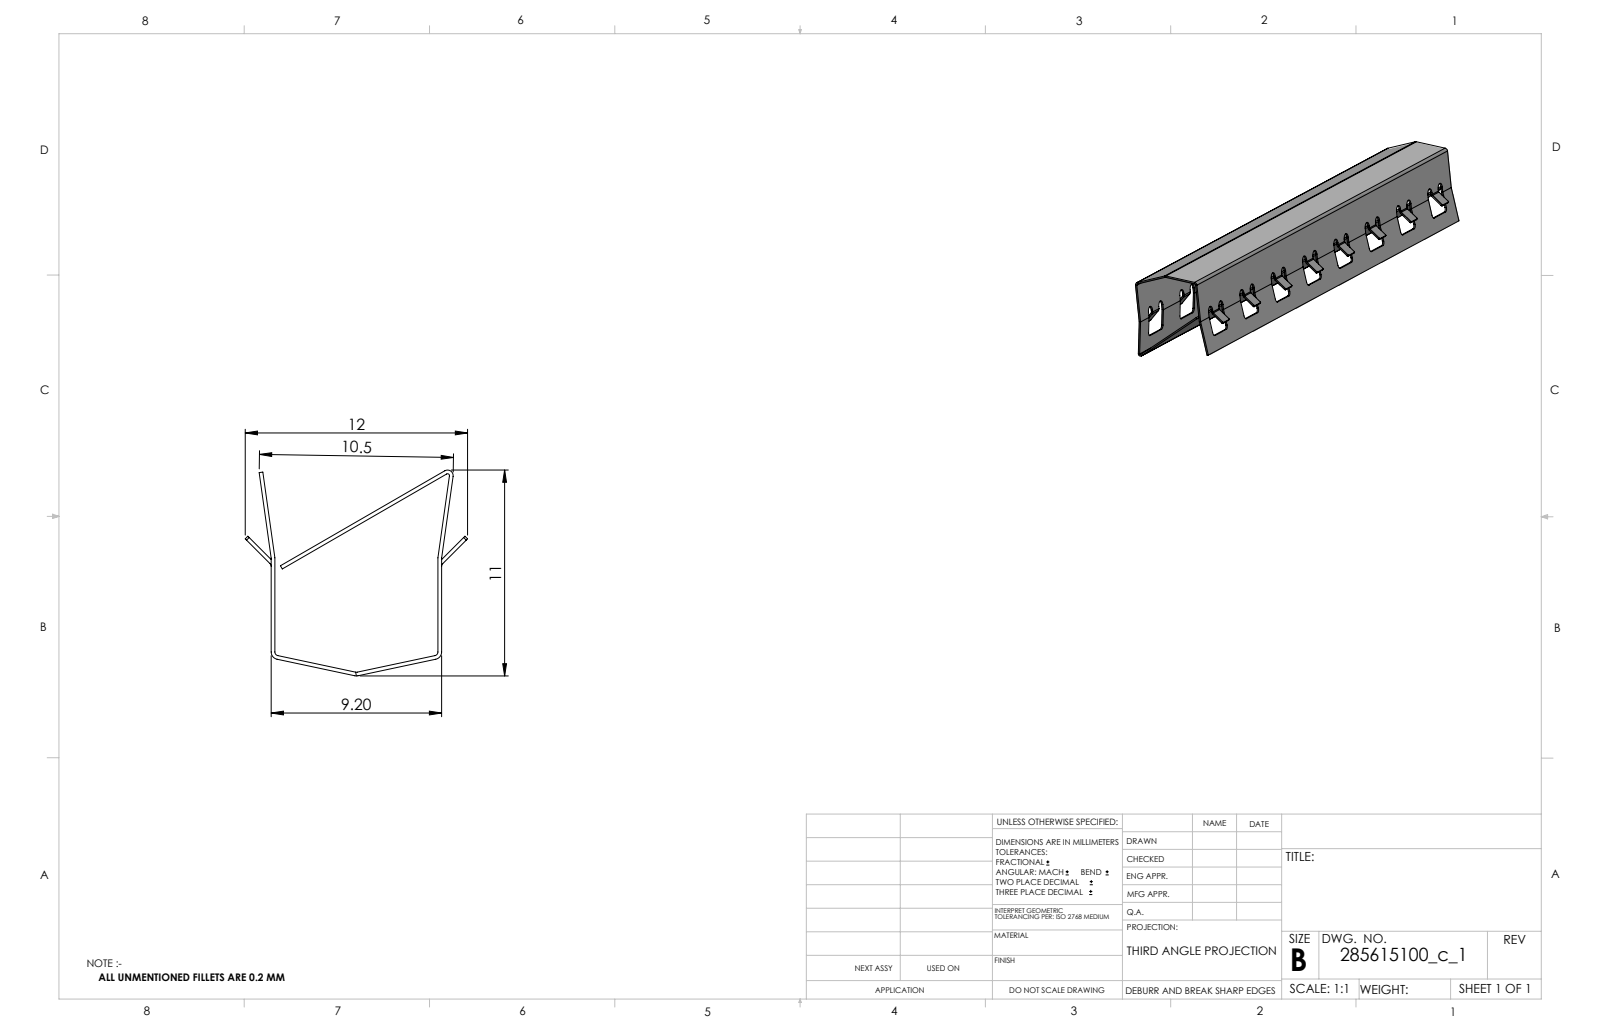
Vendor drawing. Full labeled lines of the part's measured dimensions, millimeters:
Part name (STEP PRODUCT): 285615100_c_1
STEP written by: SolidWorks 2014 (CONFIG_CONTROL_DESIGN)
Units: millimetres
Bodies: 1 solid, 298 faces (146 planar, 152 cylindrical, 0 other)
Overall size (bounding box): 80 × 12 × 11.11
Volume: 594 mm³ · Surface area: 6 053 mm²
Partial cylindrical surfaces — rounded edges, fillets, slot ends (radius × count): R0.1 ×33, R0.5 ×16, R0.65 ×16, R0.2 ×5, R0.4 ×5, R0.3 ×1
Main face-to-face distances: 9, 8.8, 9.2, 10, 20, 30, 40, 4.6, 5.4, 14.6
